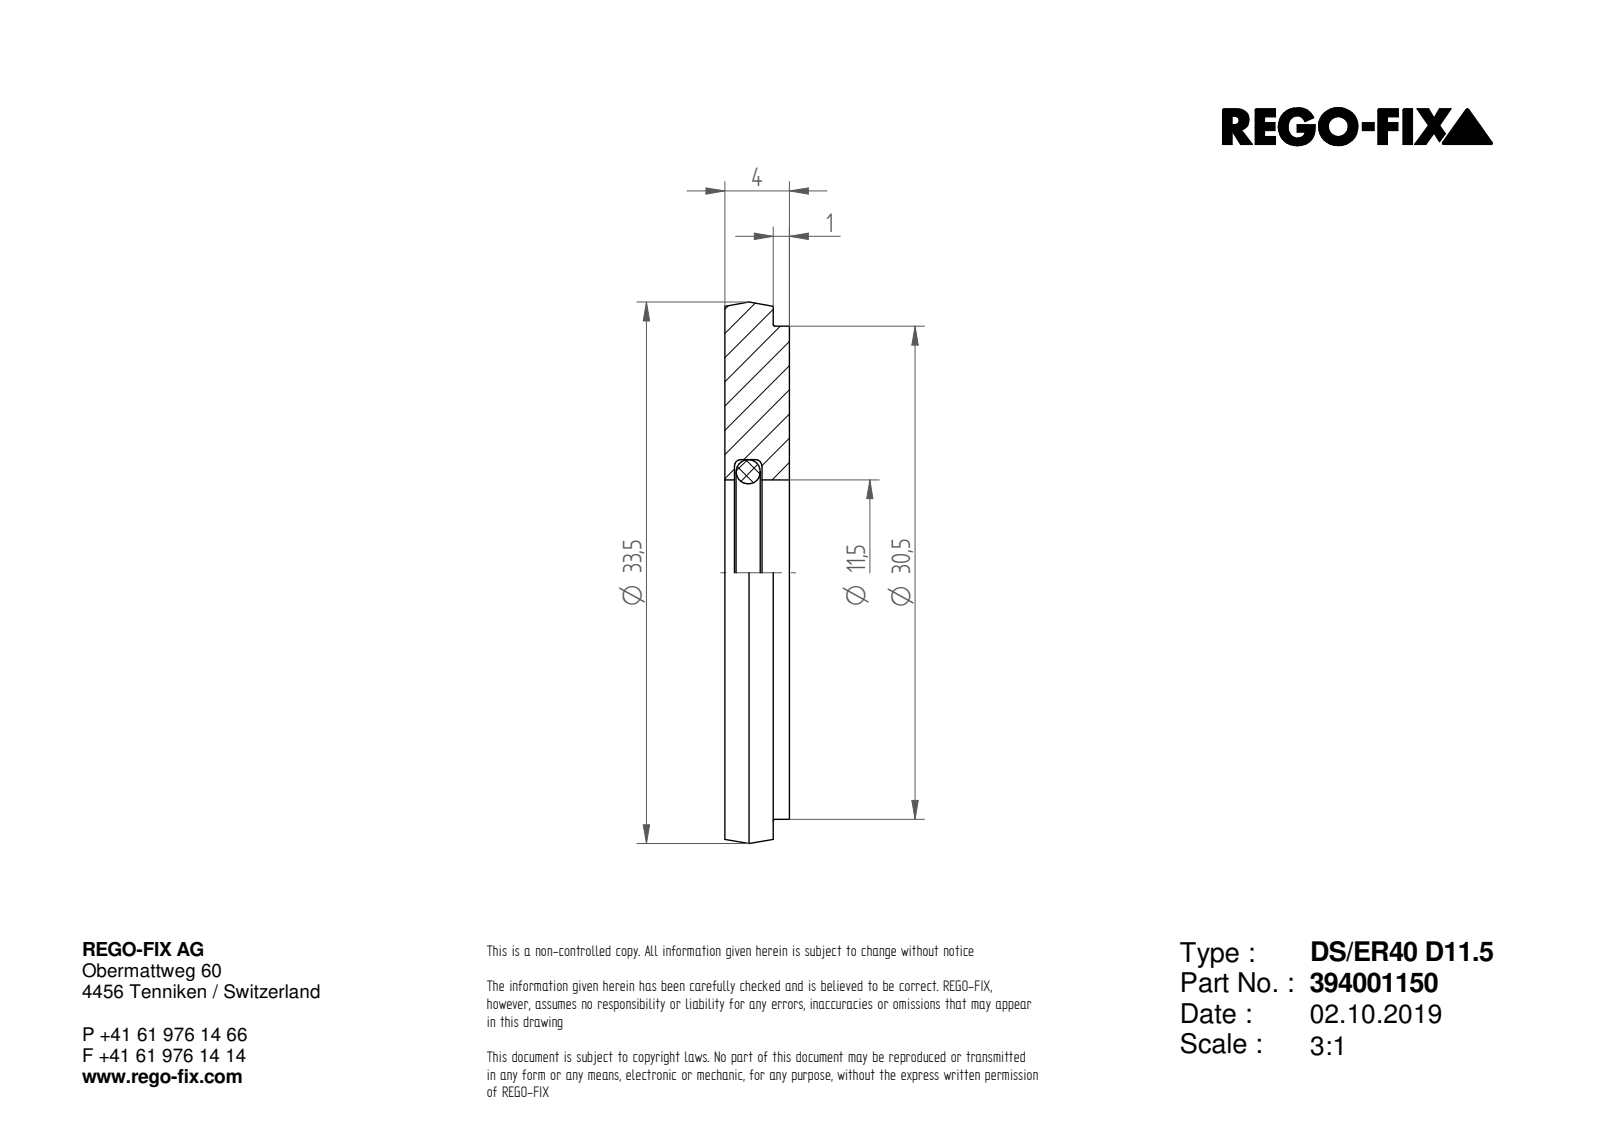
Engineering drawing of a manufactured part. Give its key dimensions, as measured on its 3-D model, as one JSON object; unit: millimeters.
{"part_name": "NOCUT", "step_written_by": "SIEMENS PLM Software Solid Edge ST10 (AUTOMOTIVE_DESIGN)", "units": "millimeters", "bodies": {"solids": 1, "faces": 7, "planar": 3, "cylindrical": 3, "other": 1}, "overall_size": [33.5, 33.5, 4], "volume_mm3": 2960, "surface_area_mm2": 2107, "round_holes": [[11.5, 1]], "round_bosses_or_shafts": [[33.5, 1], [30.5, 1]], "face_to_face_distances": [4, 1, 3]}
